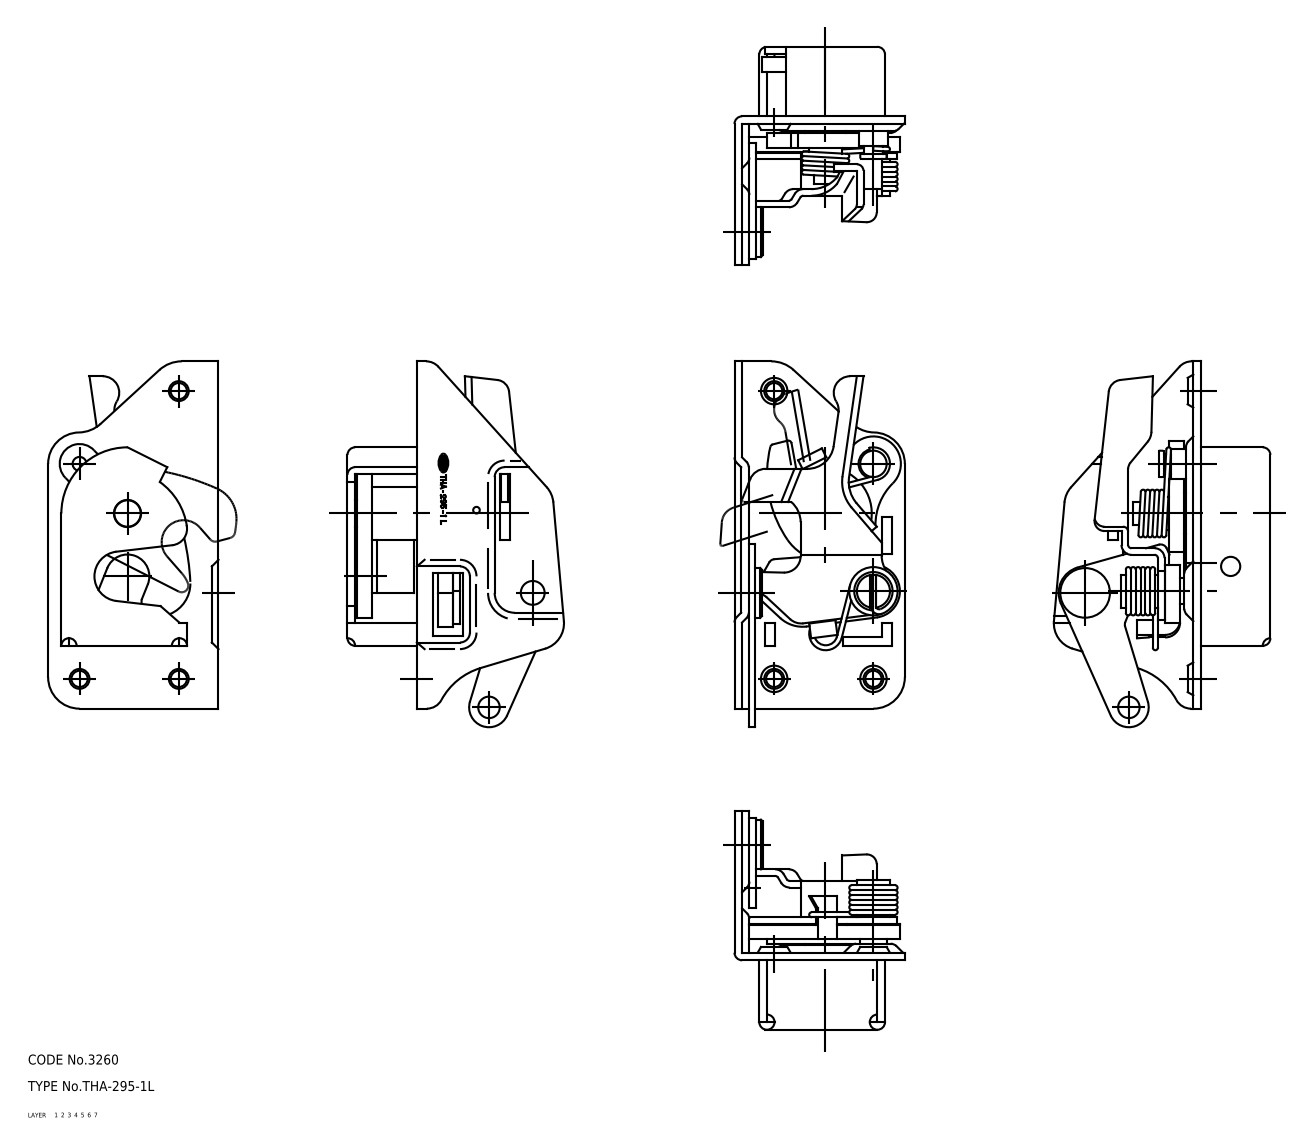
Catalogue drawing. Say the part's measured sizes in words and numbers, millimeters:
The part is named "spring_B_mr; spring_A_mr; pin_C_mr; pin_B_mr (+8 more)". Its 3-D file was written by "CADfix (AUTOMOTIVE_DESIGN)". It is 12 solids with 558 faces: 0 planar, 0 cylindrical and 558 other. Overall it measures 110.61 by 65.45 by 51.5 millimeters. Its volume is 52 067 cubic millimeters and its surface area 45 368 square millimeters.
